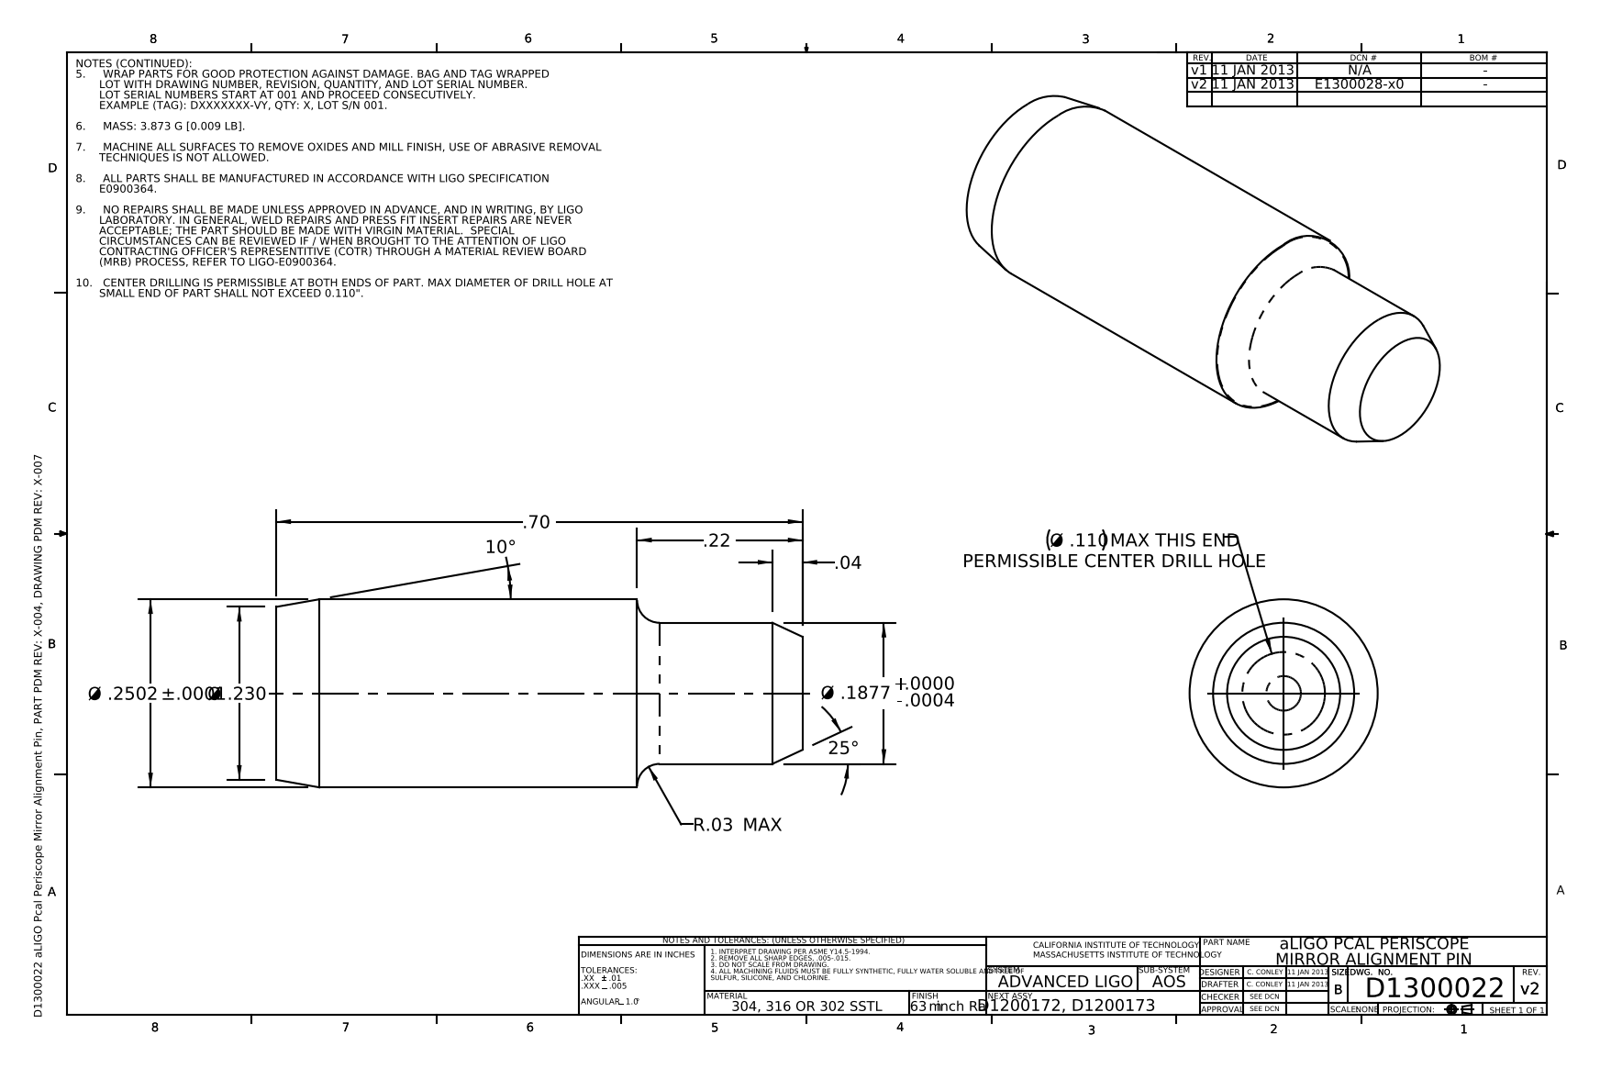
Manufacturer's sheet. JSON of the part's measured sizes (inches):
{"part_name": "D1300022-v2 aLIGO Pcal Periscope Mirror Alignment Pin", "step_written_by": "SolidWorks 2012 (AUTOMOTIVE_DESIGN)", "units": "inches", "bodies": {"solids": 1, "faces": 13, "planar": 3, "cylindrical": 4, "other": 6}, "overall_size": [0.7, 0.25, 0.25], "volume_in3": 0.029, "surface_area_in2": 0.579, "round_bosses_or_shafts": [[0.25, 1], [0.188, 1]], "face_to_face_distances": [0.7, 0.48, 0.22]}
